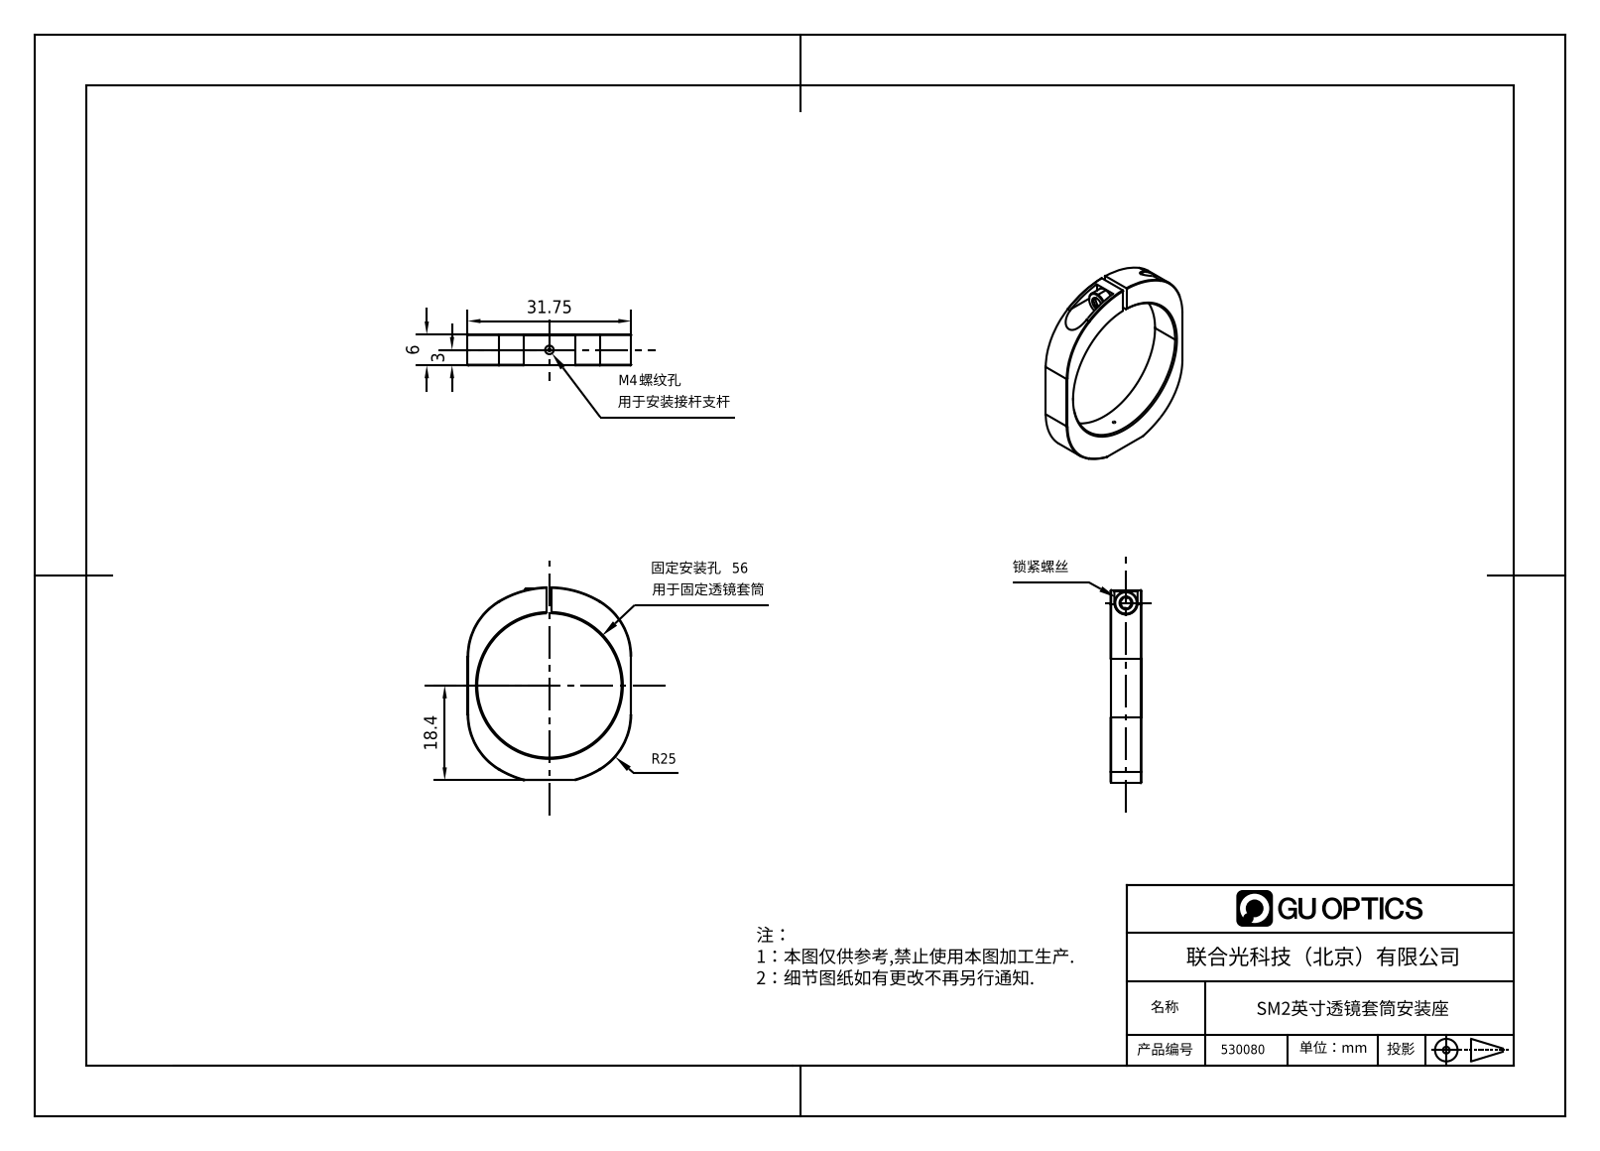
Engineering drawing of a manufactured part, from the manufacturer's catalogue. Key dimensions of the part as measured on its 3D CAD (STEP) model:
Part name (STEP PRODUCT): 1.7.6.4_ZTL-Z2_SM2英寸透镜套筒安装座
STEP written by: SolidWorks 2018 (CONFIG_CONTROL_DESIGN)
Units: millimetres
Bodies: 0 solids, 67 faces (23 planar, 18 cylindrical, 26 other)
Overall size (bounding box): 74.89 × 63.5 × 12
Round holes (diameter × count): ⌀3.3 ×1, ⌀4.2 ×1, ⌀56 ×1
Round bosses / shafts (diameter × count): ⌀8.8 ×1
Partial cylindrical surfaces — rounded edges, fillets, slot ends (radius × count): R25 ×4, R4.5 ×1, R38.1 ×1
Main face-to-face distances: 12, 63.5, 30.75, 32.75, 10.5, 2, 1.5, 4, 9, 36.75
